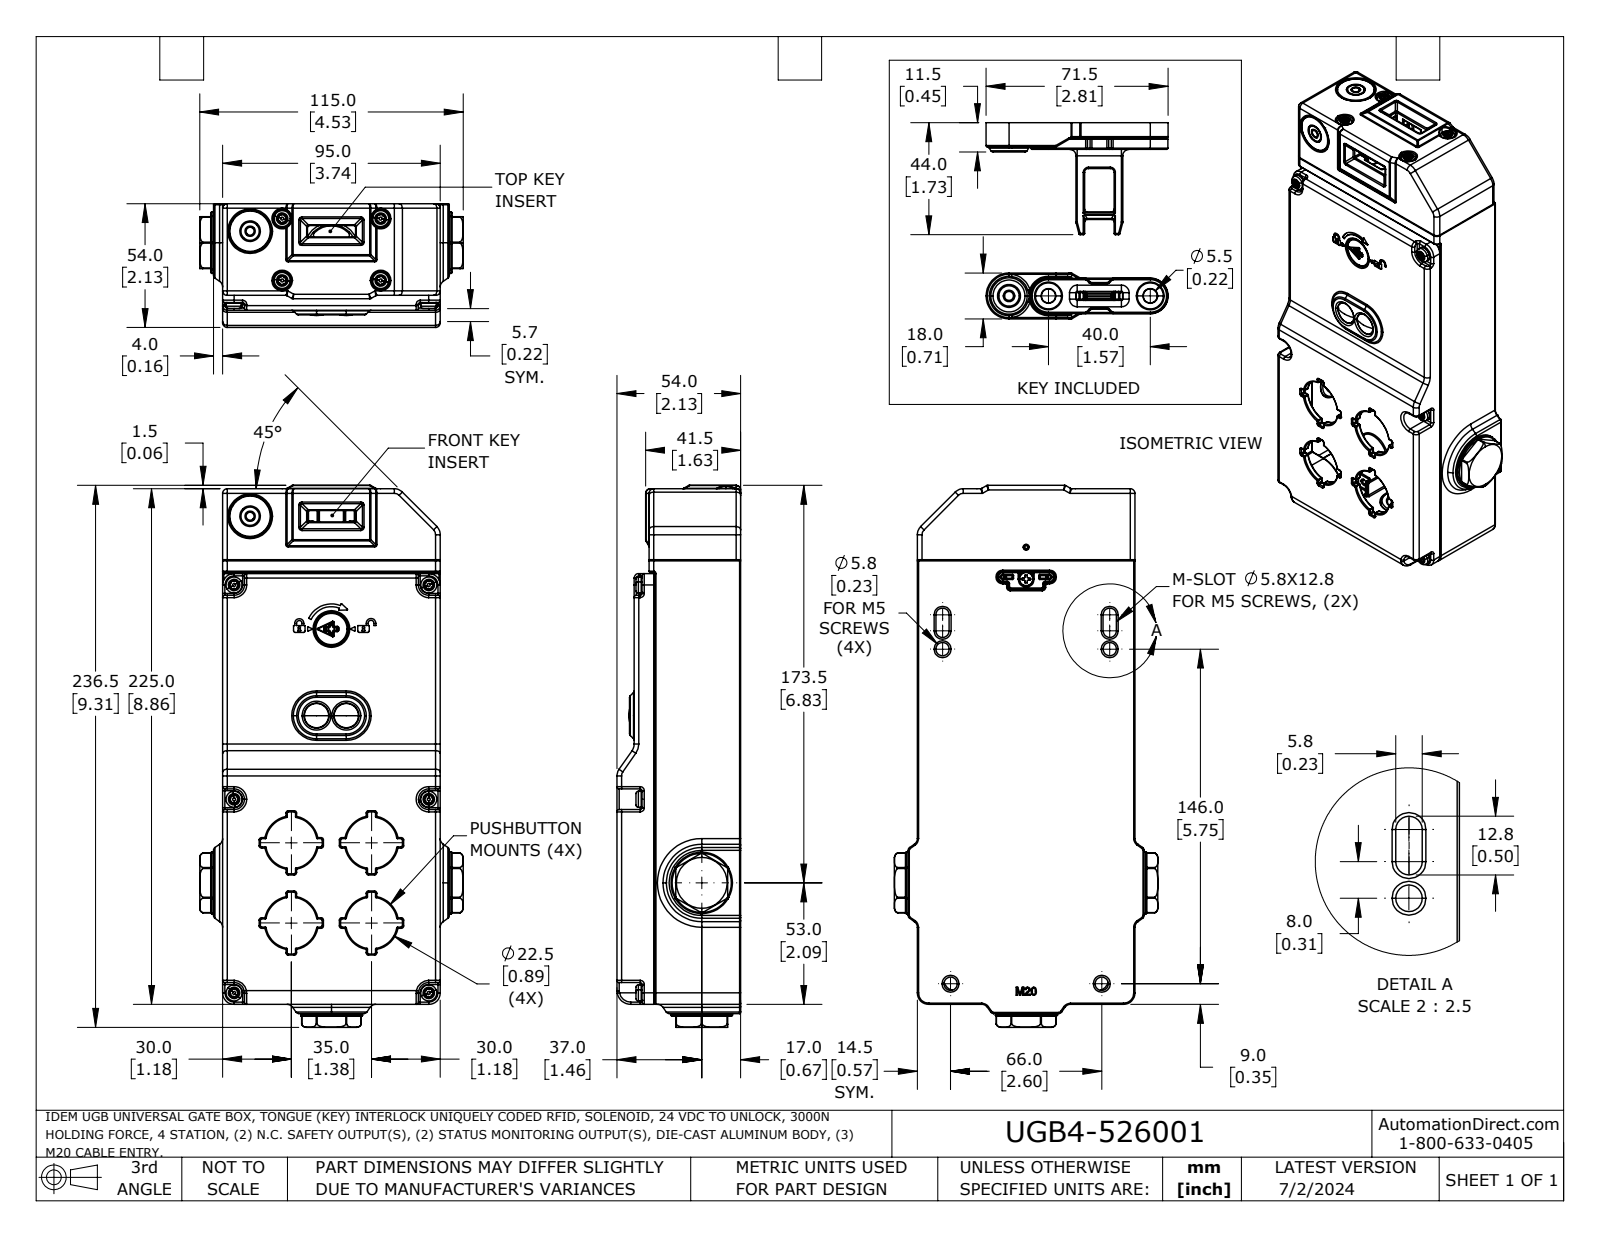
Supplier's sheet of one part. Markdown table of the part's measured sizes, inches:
| quantity | value |
| --- | --- |
| part name | 526001 UGB4-KLTM-RFID with Manual Release |
| STEP written by | SolidWorks 2021 (CONFIG_CONTROL_DESIGN) |
| units | inches |
| bodies | 26 solids, 5265 faces (1171 planar, 2169 cylindrical, 1925 other) |
| overall size | 9.803 × 4.528 × 2.126 |
| volume | 18.95 in³ |
| surface area | 304.5 in² |
| round holes (diameter × count) | 0.13 × 10, 0.157 × 10, 0.098 × 8, 0.177 × 8, 0.315 × 8, 0.165 × 4, 0.197 × 4, 0.217 × 4, 0.228 × 4, 0.472 × 4, 0.354 × 3, 0.087 × 2 |
| round bosses / shafts (diameter × count) | 0.138 × 12, 0.276 × 10, 0.051 × 10, 0.244 × 6, 0.236 × 5, 0.709 × 3, 1.055 × 2, 0.764 × 2 |
| partial cylindrical surfaces (radius × count) | 0.02 × 650, 0.039 × 205, 0.008 × 127, 0.012 × 122, 0.079 × 36, 0.016 × 22, 0.028 × 20, 0.031 × 16 |
| main face-to-face distances | 0.118, 0.087, 3.622, 0.295, 3.74, 2.008, 2.126, 2.039, 0.177, 1.831 |
| hole center spacings | 1, 1.648, 0.61, 1.433, 2.284, 3.346, 0.111, 0.187 |
